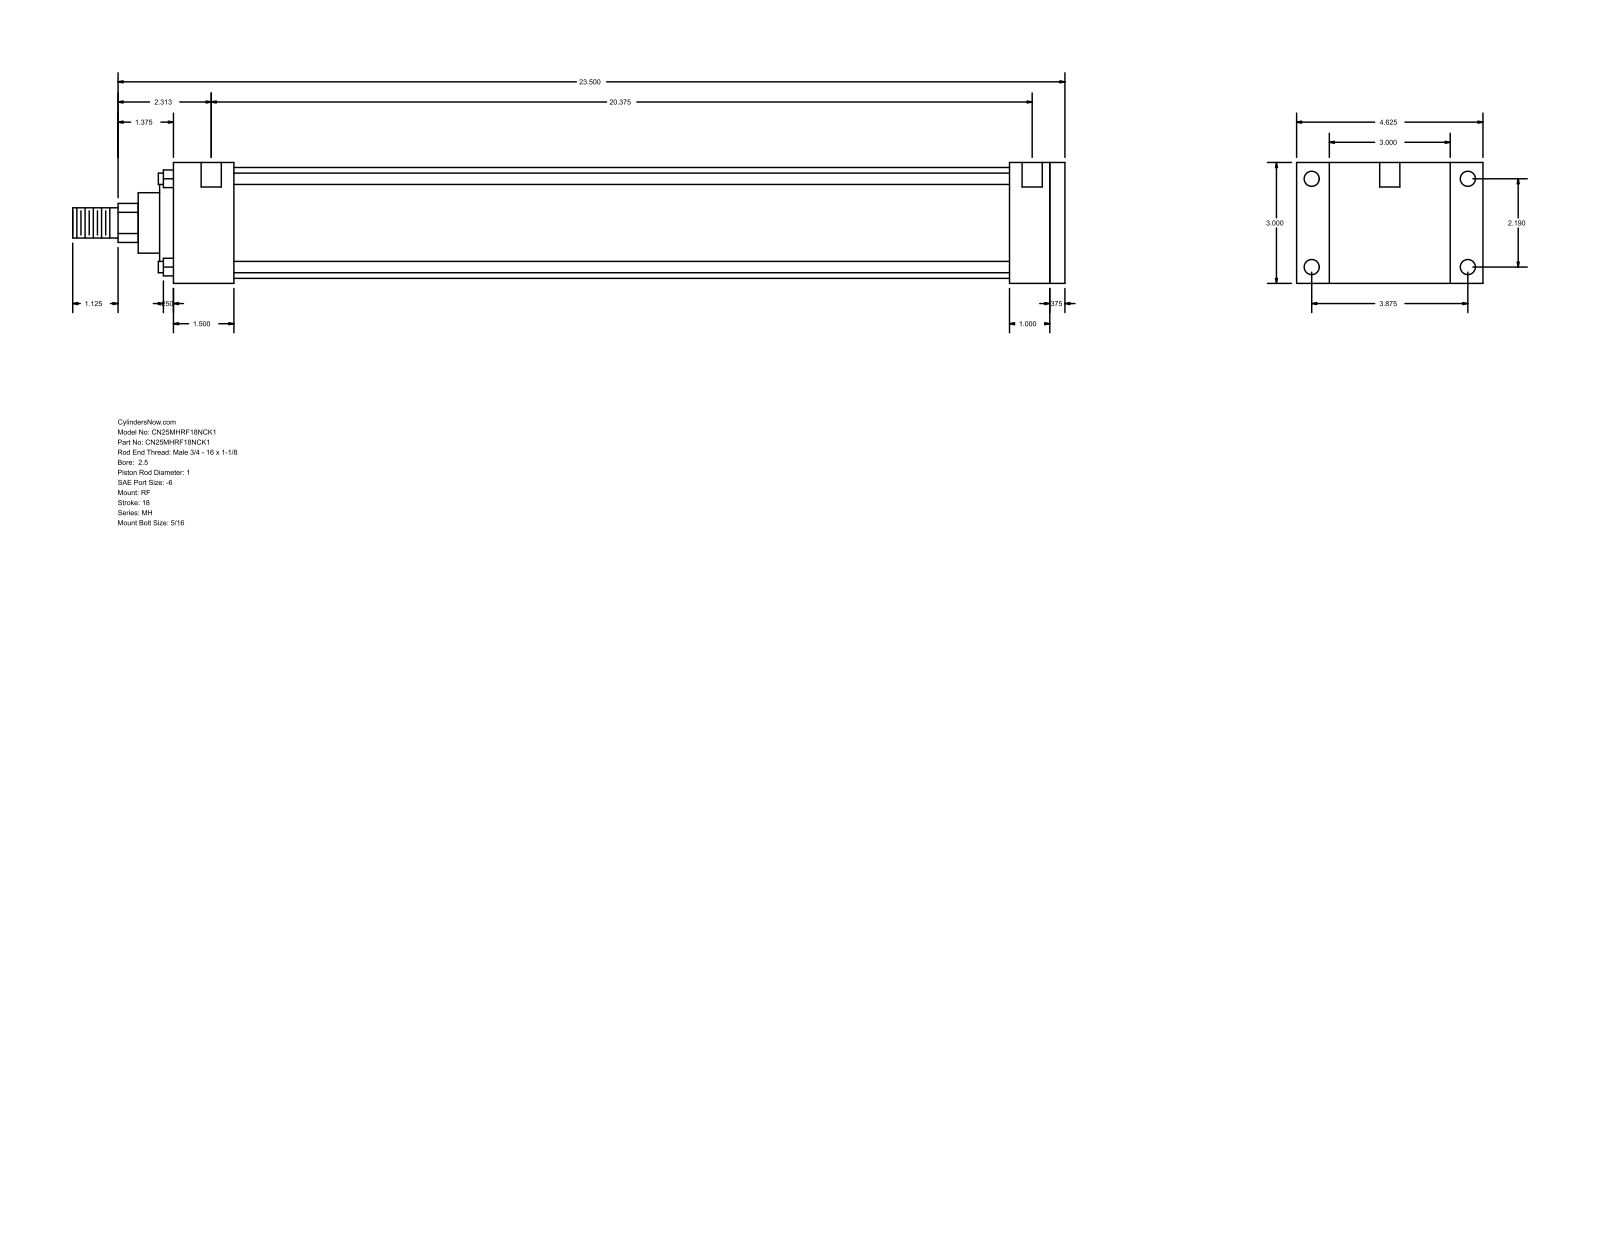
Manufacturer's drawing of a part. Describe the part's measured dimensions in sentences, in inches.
The part is named "MH_RF__0250_1". Its 3-D file was written by "GSSL Pune (CONFIG_CONTROL_DESIGN)". It is 0 solids with 94 faces: 65 planar, 29 cylindrical and 0 other. Overall it measures 24.625 by 4.625 by 3 inches. Round holes: 4 of diameter 0.219, 4 of diameter 0.375, 2 of diameter 0.5. Round bosses or shafts: 4 of diameter 0.281, 1 of diameter 2.75, 1 of diameter 2.375, 1 of diameter 1.5, 1 of diameter 1, 1 of diameter 0.75. Partial cylindrical surfaces (rounded edges, fillets, slot ends): 1 of radius 0.484. The main face-to-face distances are 3, 0.375, 22.125, 21.75, 1, 1.375, 20.75, 1.5, 19.25, 20.25. The hole center spacings are 2.19, 3.875, 4.451, 20.687, 0.125, 0.187, 20.375, 20.5.
